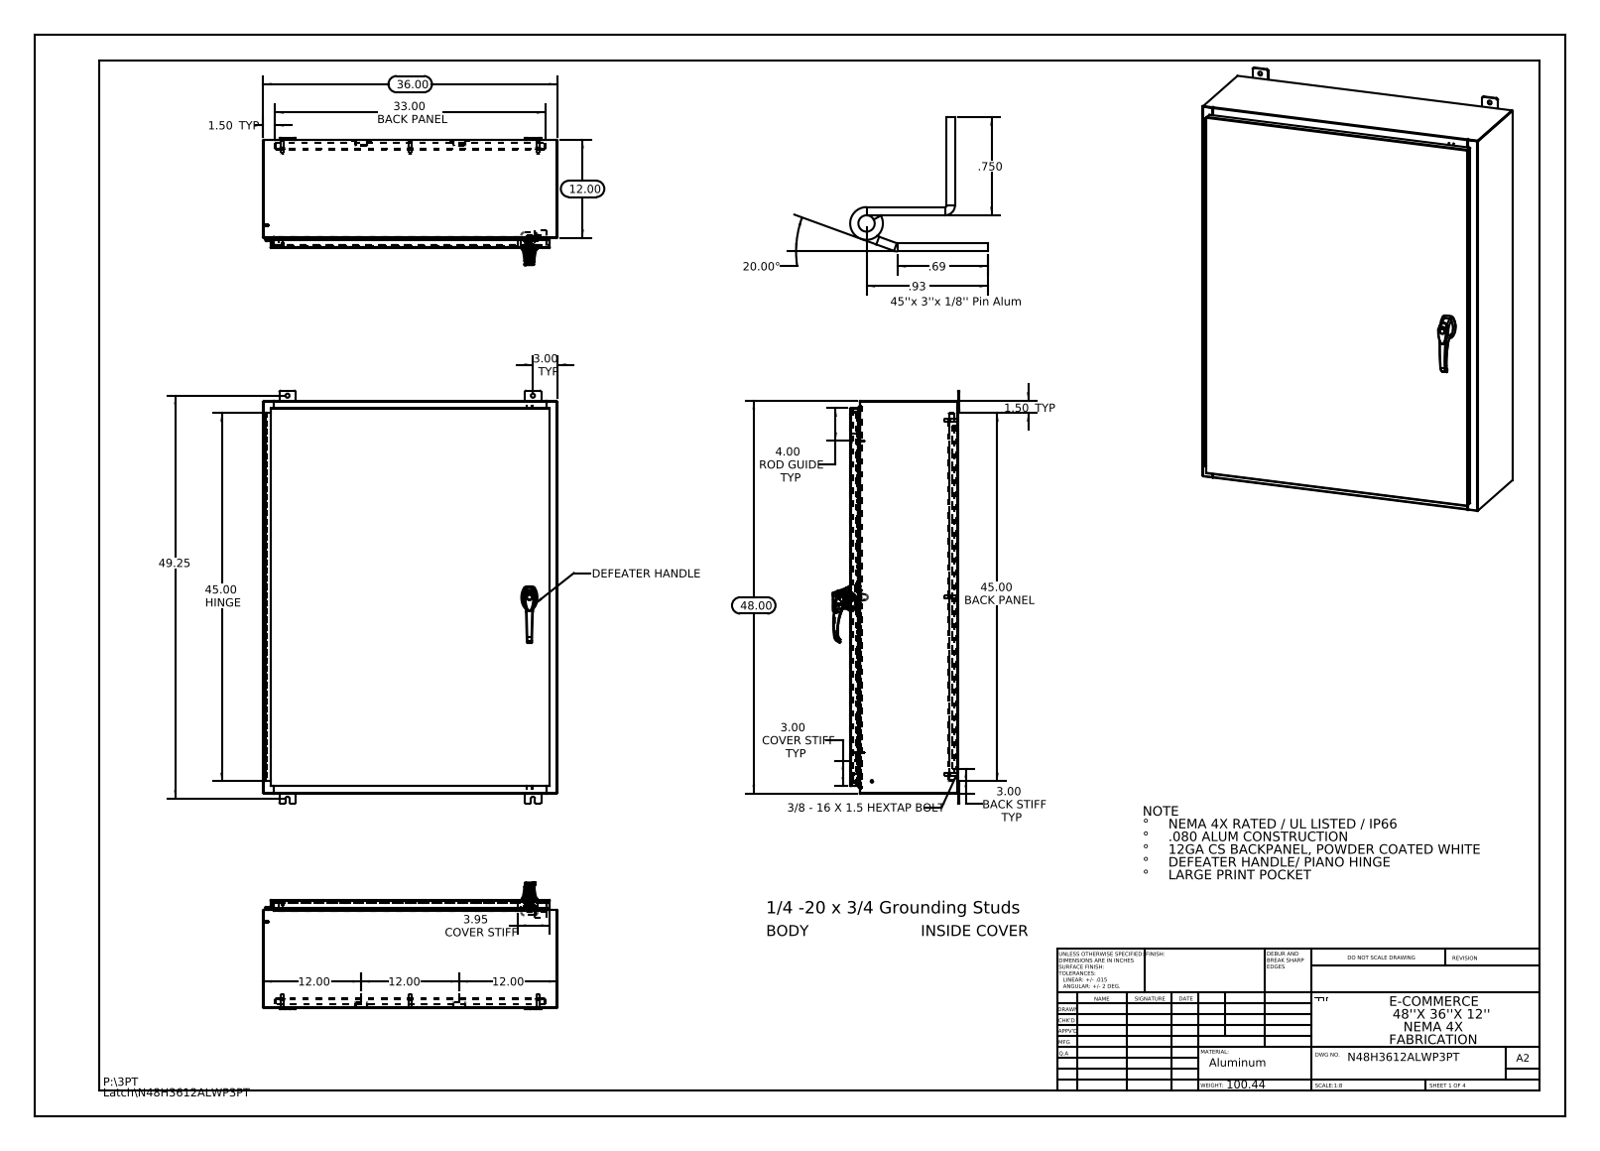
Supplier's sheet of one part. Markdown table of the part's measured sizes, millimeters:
| quantity | value |
| --- | --- |
| part name | N48H3612ALWP3PT Enclosure Stiffener; N48H3612ALWP3PT Bottom; Quarter-20 CD Stud; 022151 (+8 more) |
| STEP written by | SolidWorks 2013 (CONFIG_CONTROL_DESIGN) |
| units | millimeters |
| bodies | 51 solids, 3400 faces (1309 planar, 1305 cylindrical, 786 other) |
| overall size | 1282.7 × 914.4 × 393.6 |
| volume | 10 750 000 mm³ |
| surface area | 10 520 000 mm² |
| round holes (diameter × count) | 12.7 × 12, 6.4 × 10, 3.5 × 3, 4.1 × 3, 2 × 2, 5.2 × 2, 8 × 2, 11.1 × 2, 3.2 × 1, 3.2 × 1, 5 × 1, 7 × 1 |
| round bosses / shafts (diameter × count) | 4 × 10, 3.6 × 10, 15.9 × 8, 9.5 × 8, 8.4 × 8, 8 × 3, 6 × 3, 30 × 1 |
| partial cylindrical surfaces (radius × count) | 3 × 37, 0.3 × 34, 0.2 × 33, 2.2 × 28, 4.8 × 24, 1 × 15, 0.7 × 12, 0.2 × 6 |
| main face-to-face distances | 1.9, 333.4, 331.5, 335.3, 2.6, 25.4, 308, 27.3, 306.1, 29.9 |
| hole center spacings | 440.9, 499.5, 549.3, 965.3, 1168, 793.8, 1098.6, 7.5 |
